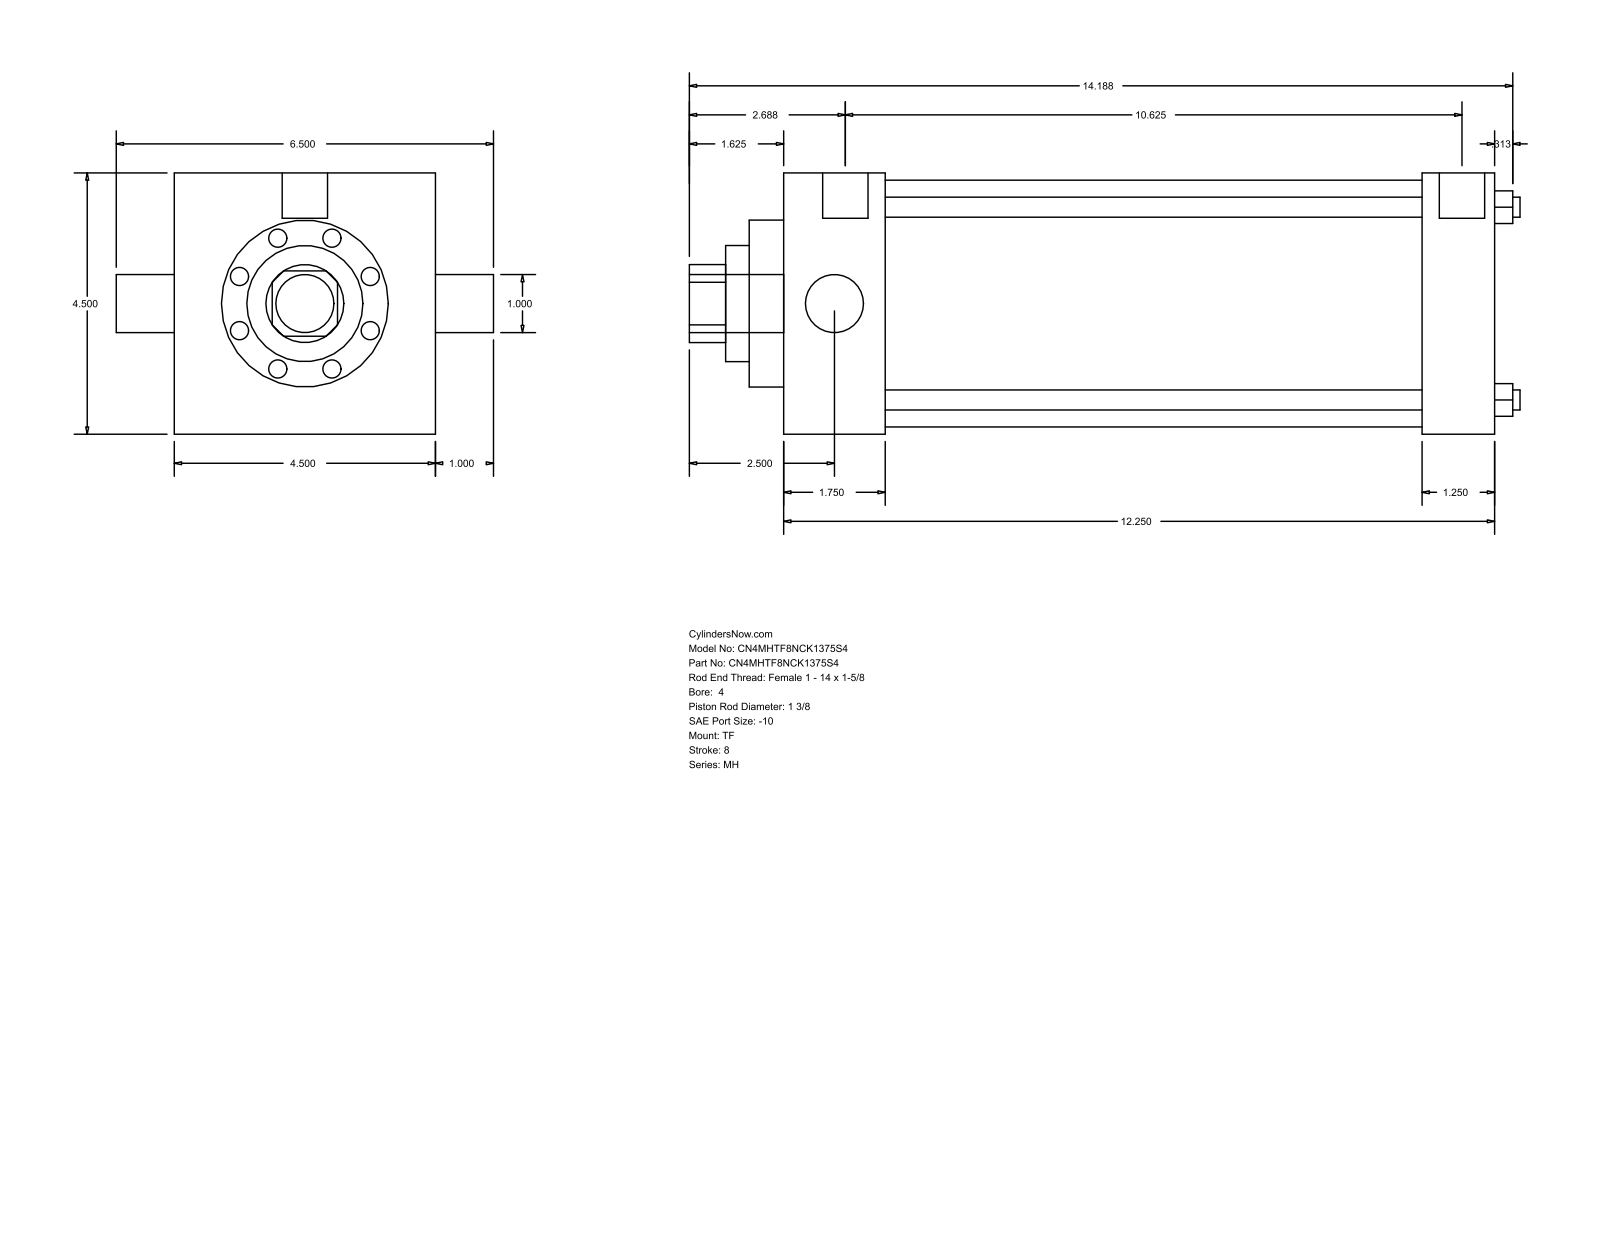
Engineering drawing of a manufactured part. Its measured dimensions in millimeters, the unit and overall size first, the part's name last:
Units: millimetres
Overall size (bounding box): 363.54 × 165.1 × 114.3
Round holes (diameter × count): ⌀8.76 ×4, ⌀25.4 ×1, ⌀34.92 ×1, ⌀50.8 ×1, ⌀73.03 ×1, ⌀107.95 ×1
Round bosses / shafts (diameter × count): ⌀8.73 ×3, ⌀19.84 ×2, ⌀25.4 ×1
Partial cylindrical surfaces — rounded edges, fillets, slot ends (radius × count): R17.06 ×1
Main face-to-face distances: 114.3, 311.16, 44.45, 266.71, 279.41, 234.96, 31.75, 15.08, 59.53, 294.49
Hole centre spacings: 59.62, 84.32, 119.25
Bodies: 0 solids, 86 faces (61 planar, 25 cylindrical, 0 other)
Part name (STEP PRODUCT): MH_TF__0400_1.375
STEP written by: GSSL Pune (CONFIG_CONTROL_DESIGN)
